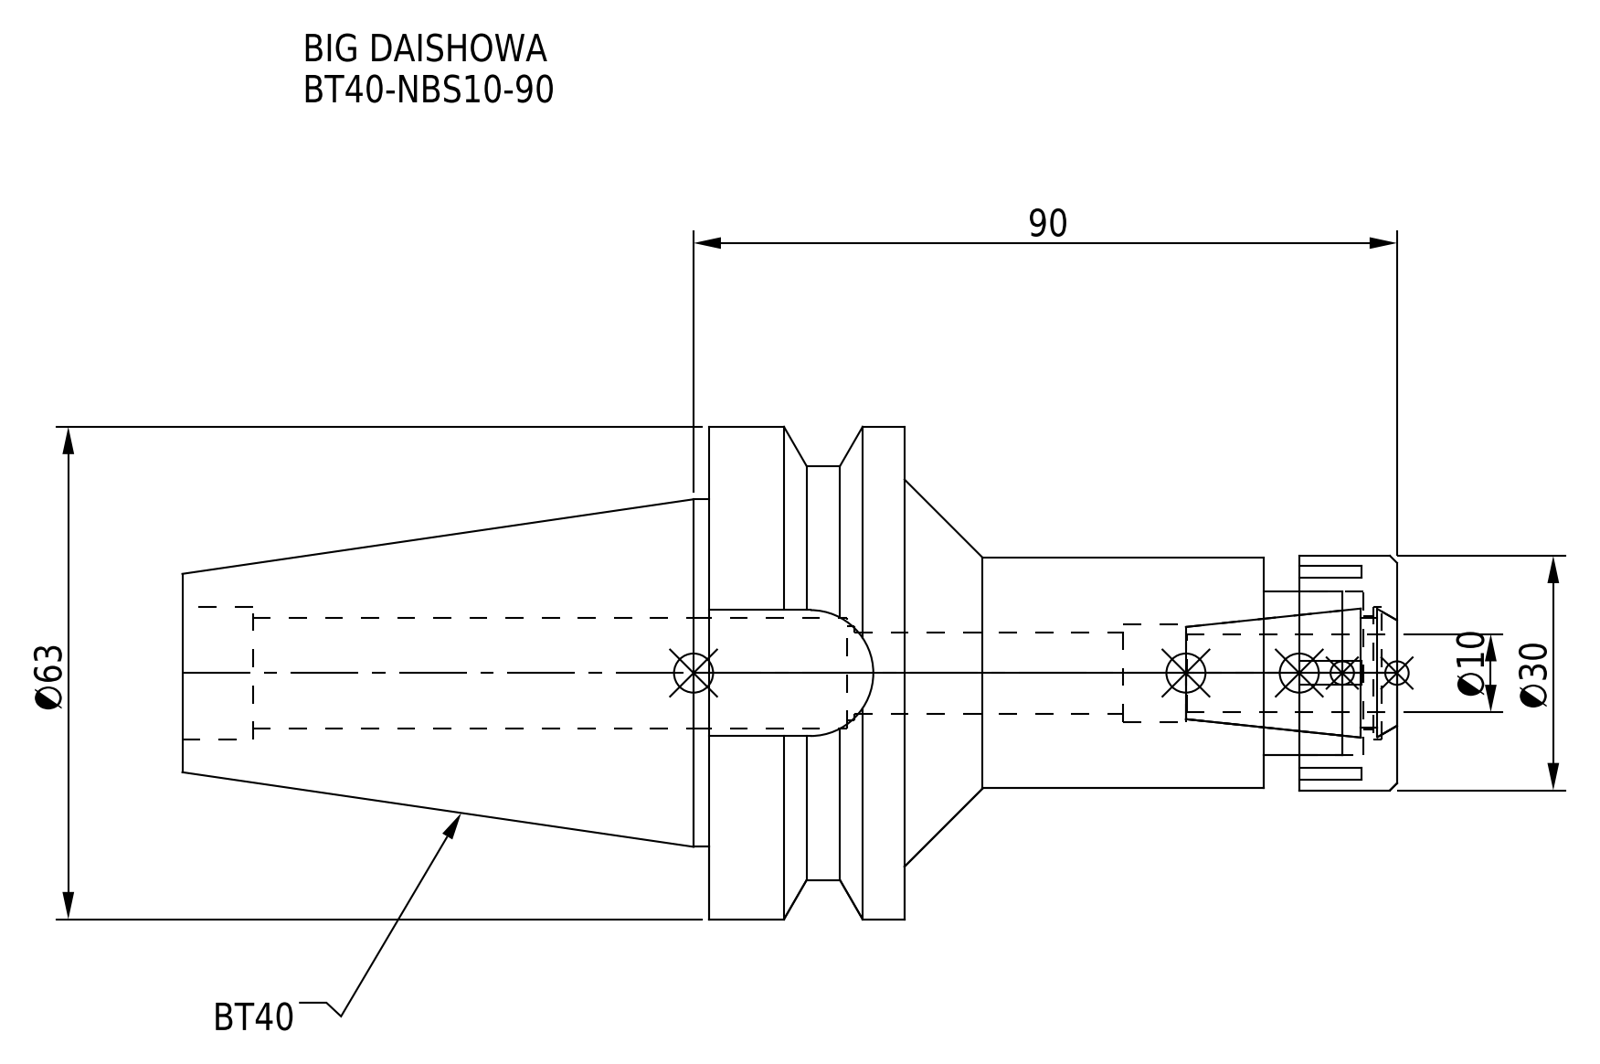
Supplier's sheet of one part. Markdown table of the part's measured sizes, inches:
| quantity | value |
| --- | --- |
| part name | DXF_TEMP_ASSY_ASM_4_ASM.stp; NBN10_1.stp; BT40-NBS10-90-FreeParts; BT40-NBS10-90.stp (+3 more) |
| STEP written by | SolidWorks 2019 (CONFIG_CONTROL_DESIGN) |
| units | inches |
| bodies | 2 solids, 93 faces (45 planar, 34 cylindrical, 14 other) |
| overall size | 6.118 × 2.48 × 2.48 |
| volume | 9.68 in³ |
| surface area | 50.36 in² |
| round holes (diameter × count) | 0.409 × 1, 0.472 × 1, 0.492 × 1, 0.559 × 1, 0.571 × 1, 0.669 × 1, 0.827 × 1 |
| round bosses / shafts (diameter × count) | 2.48 × 1, 2.087 × 1, 1.75 × 1, 1.181 × 1, 1.161 × 1 |
| partial cylindrical surfaces (radius × count) | 0.317 × 1 |
| main face-to-face distances | 0.984, 2.48, 3.465, 0.177, 0.492, 2.654, 0.669, 1.811, 2.795, 1.988 |
